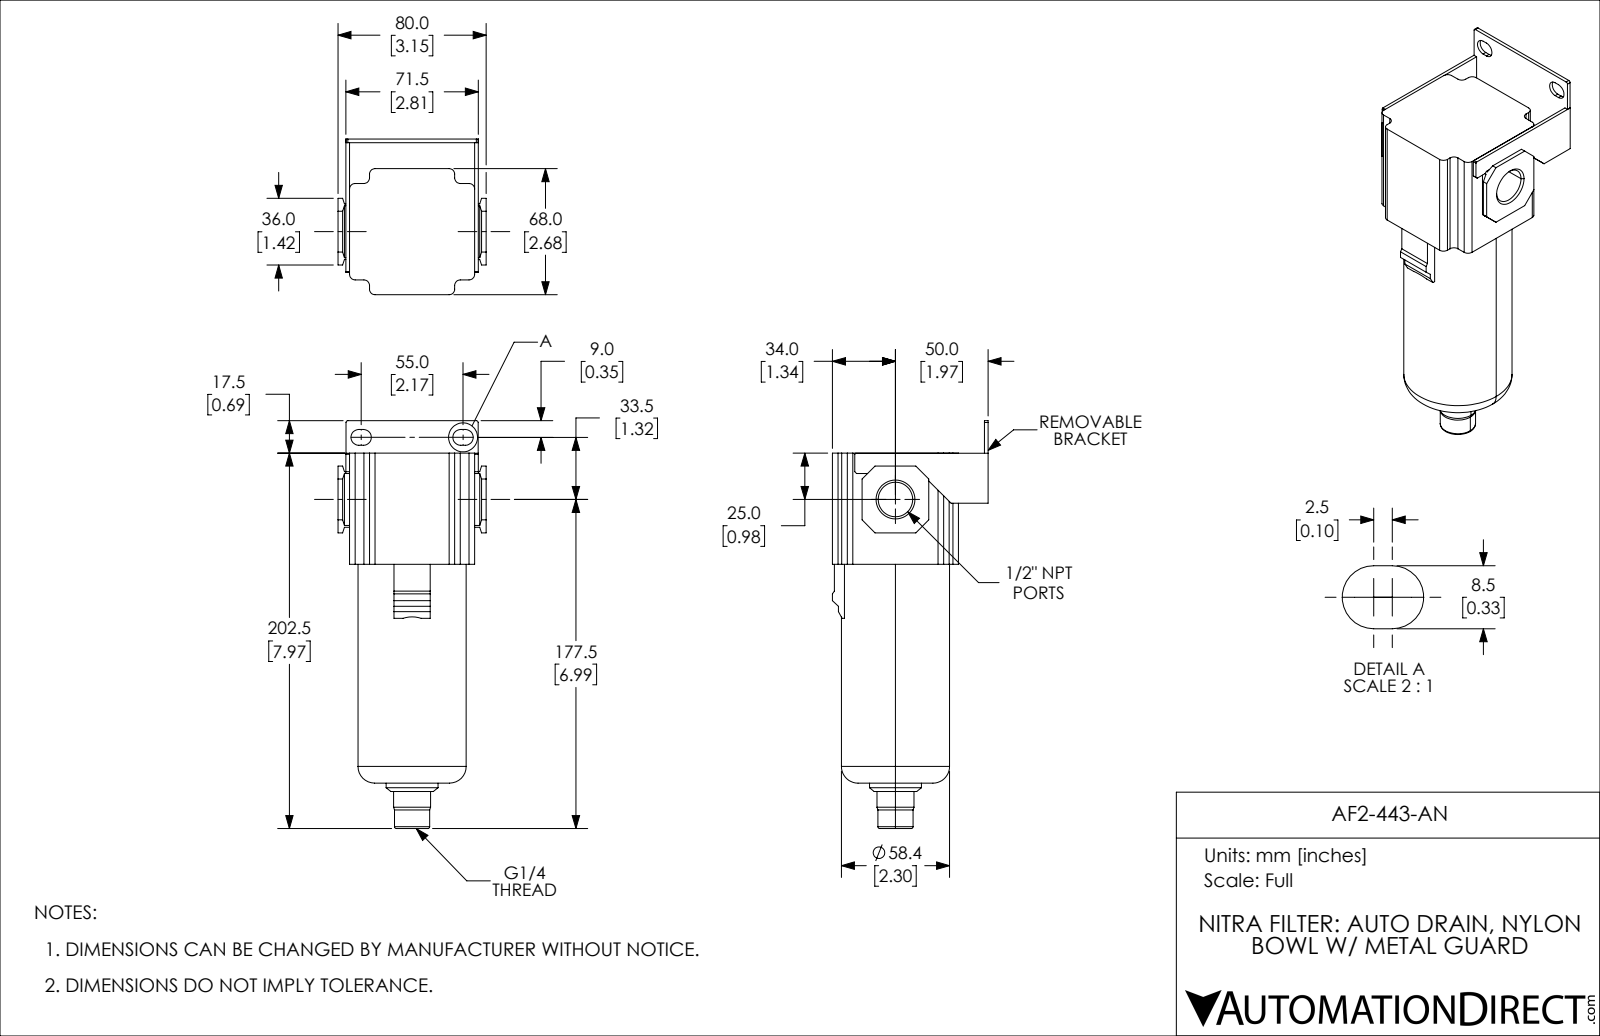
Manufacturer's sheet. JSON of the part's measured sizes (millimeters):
{"part_name": "AF2-443-AN", "step_written_by": "SolidWorks 2019 (CONFIG_CONTROL_DESIGN)", "units": "millimeters", "bodies": {"solids": 1, "faces": 136, "planar": 90, "cylindrical": 32, "other": 14}, "overall_size": [220, 84, 80], "volume_mm3": 589844, "surface_area_mm2": 61015, "round_holes": [[8.57, 1], [18.63, 1]], "round_bosses_or_shafts": [[58.4, 1], [28, 1], [20, 1], [19, 1]], "partial_cylinders_radius": [[3, 12], [4.25, 4], [1, 2]], "face_to_face_distances": [2, 16, 60, 68, 84, 82, 69.5, 14, 67.5, 4.25]}
